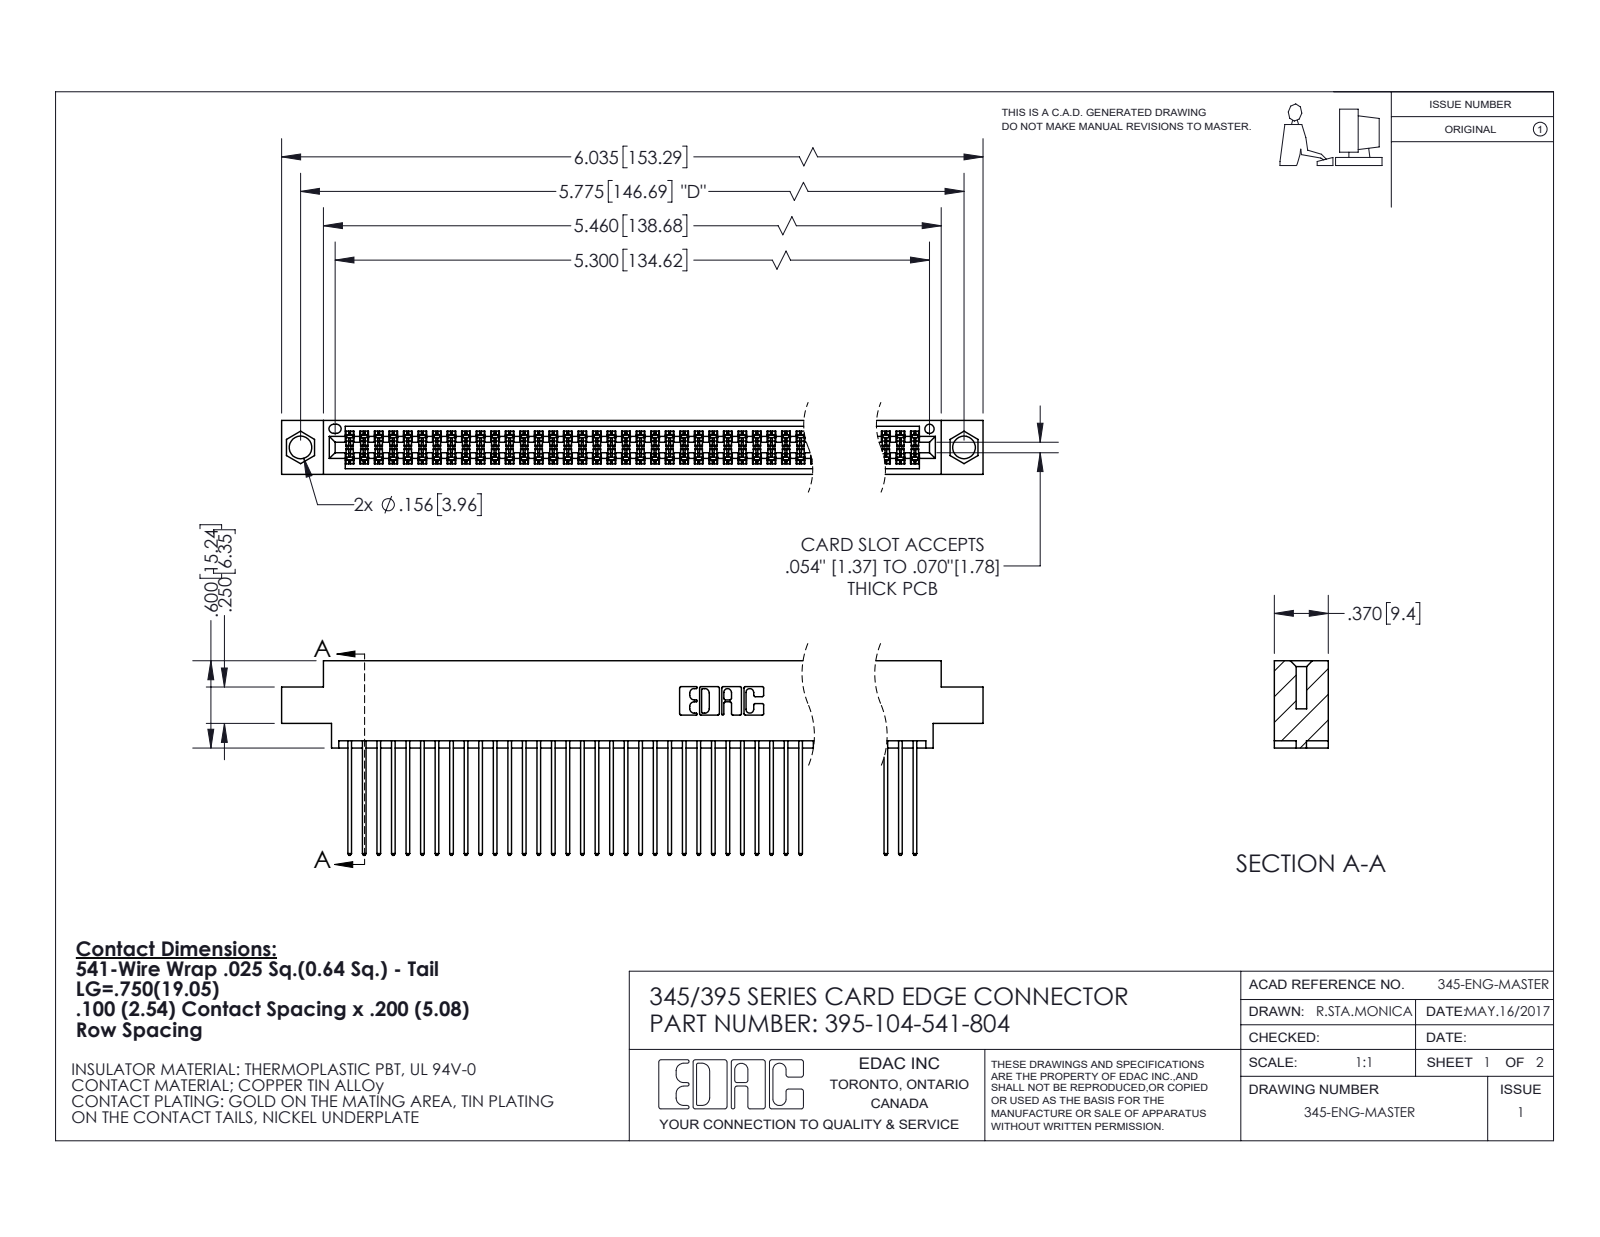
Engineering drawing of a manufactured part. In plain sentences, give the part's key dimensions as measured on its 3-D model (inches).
The part is named "395-104-541-804; 345-292-001_345-293-141; 345 Part_0.170 Offset - 0.156 Dia-TI". Its 3-D file was written by "SolidWorks 2020 (CONFIG_CONTROL_DESIGN)". It is 105 solids with 5344 faces: 3530 planar, 1814 cylindrical and 0 other. Overall it measures 6.035 by 1.337 by 0.37 inches. Its volume is 0.937 cubic inches and its surface area 39.83 square inches. Round holes: 2 of diameter 0.156, 1 of diameter 0.064. Partial cylindrical surfaces (rounded edges, fillets, slot ends): 156 of radius 0.006, 104 of radius 0.01, 22 of radius 0.01, 6 of radius 0.007, 6 of radius 0.031, 3 of radius 0.026, 2 of radius 0.014, 2 of radius 0.019. The main face-to-face distances are 0.072, 0.298, 0.2, 0.098, 0.272, 0.025, 0.225, 0.37, 0.175, 0.149. The hole center spacings are 0.27, 5.539, 5.775.
